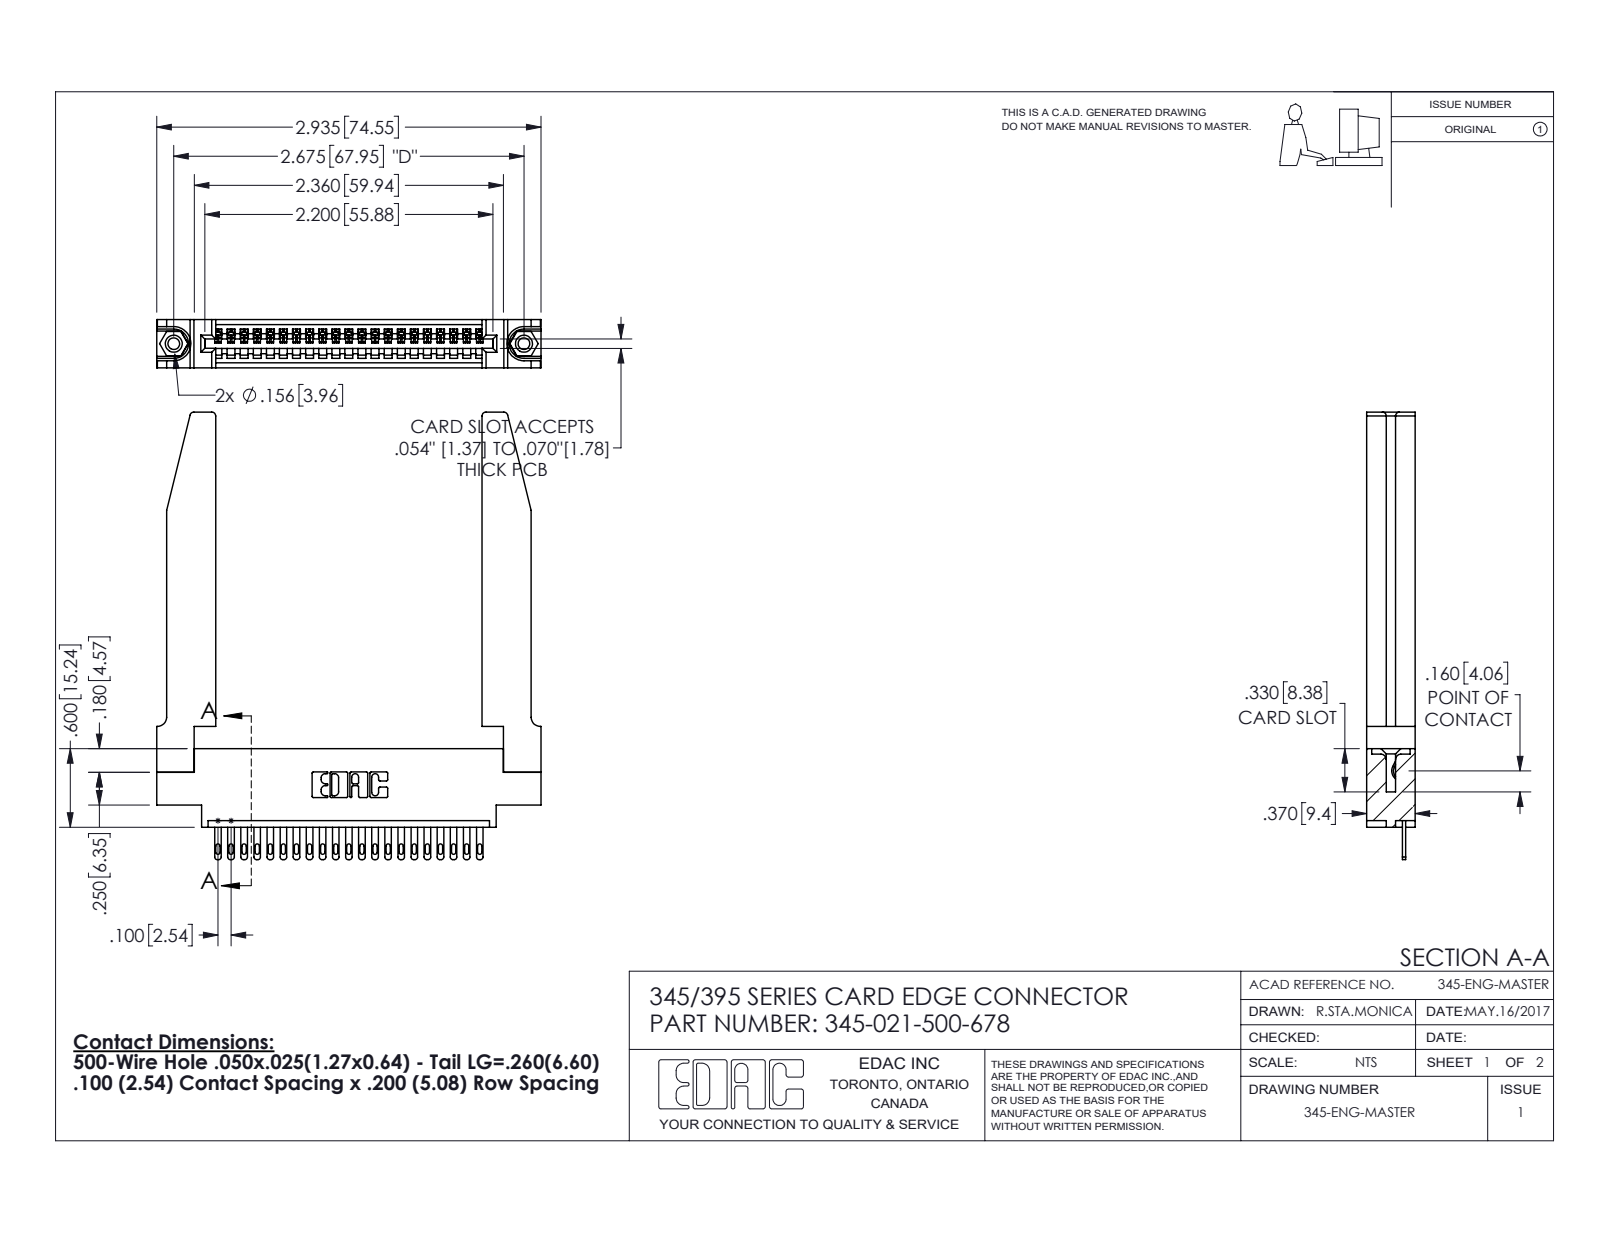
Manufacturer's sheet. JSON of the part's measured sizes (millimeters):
{"part_name": "345-021-500-678; 345-292-001_345-293-100; 345-250-001_345-250-001-102; 345-220-078_345-220-078 (+1 more)", "step_written_by": "SolidWorks 2016 (CONFIG_CONTROL_DESIGN)", "units": "millimeters", "bodies": {"solids": 26, "faces": 1498, "planar": 940, "cylindrical": 506, "other": 52}, "overall_size": [86.8, 74.6, 9.4], "volume_mm3": 14600, "surface_area_mm2": 15790, "round_holes": [[2.3, 2], [3.2, 2], [4, 2], [1.6, 1]], "round_bosses_or_shafts": [[3.9, 2]], "partial_cylinders_radius": [[0.2, 42], [0.4, 42], [0.5, 42], [0.3, 22], [0.8, 8], [0.2, 6], [0.8, 6], [0.7, 3]], "face_to_face_distances": [9.4, 1.8, 7.6, 2.5, 6.9, 0.6, 5.1, 3.8, 3.8, 5.6], "hole_center_spacings": [6.9, 62, 67.9]}
